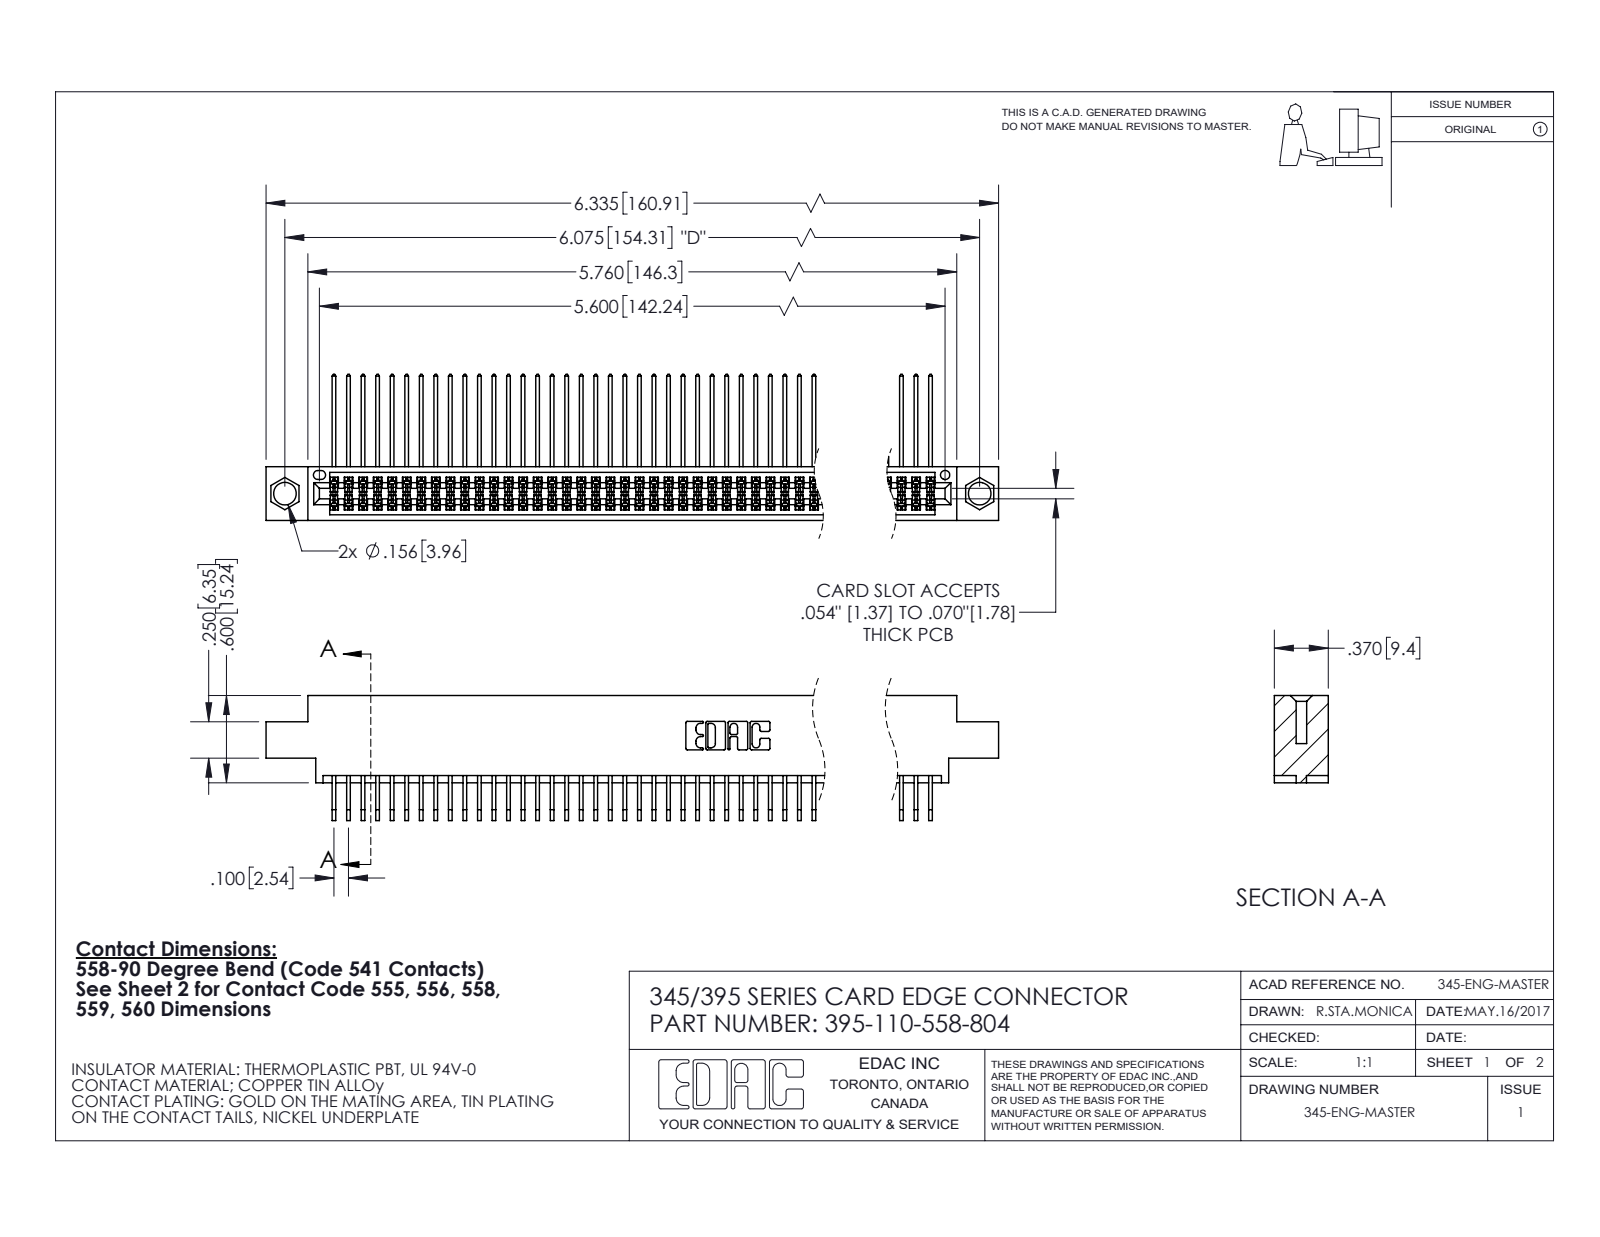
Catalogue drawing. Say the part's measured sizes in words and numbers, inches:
The part is named "345-292-001_558 Tail - 2; 395-110-558-804; 345-292-001_558 559 Tail - 1; 345 Part_0.170 Offset - 0.156 Dia-TI". Its 3-D file was written by "SolidWorks 2020 (CONFIG_CONTROL_DESIGN)". It is 111 solids with 5864 faces: 3948 planar, 1916 cylindrical and 0 other. Overall it measures 6.335 by 1.005 by 0.859 inches. Its volume is 0.987 cubic inches and its surface area 42.05 square inches. Round holes: 2 of diameter 0.156, 1 of diameter 0.064. Partial cylindrical surfaces (rounded edges, fillets, slot ends): 220 of radius 0.006, 22 of radius 0.01, 6 of radius 0.007, 6 of radius 0.031, 3 of radius 0.026, 2 of radius 0.014, 2 of radius 0.019, 2 of radius 0.022. The main face-to-face distances are 0.072, 0.298, 0.2, 0.37, 0.098, 0.272, 0.025, 0.225, 0.175, 0.025. The hole center spacings are 0.27, 5.839, 6.075.
